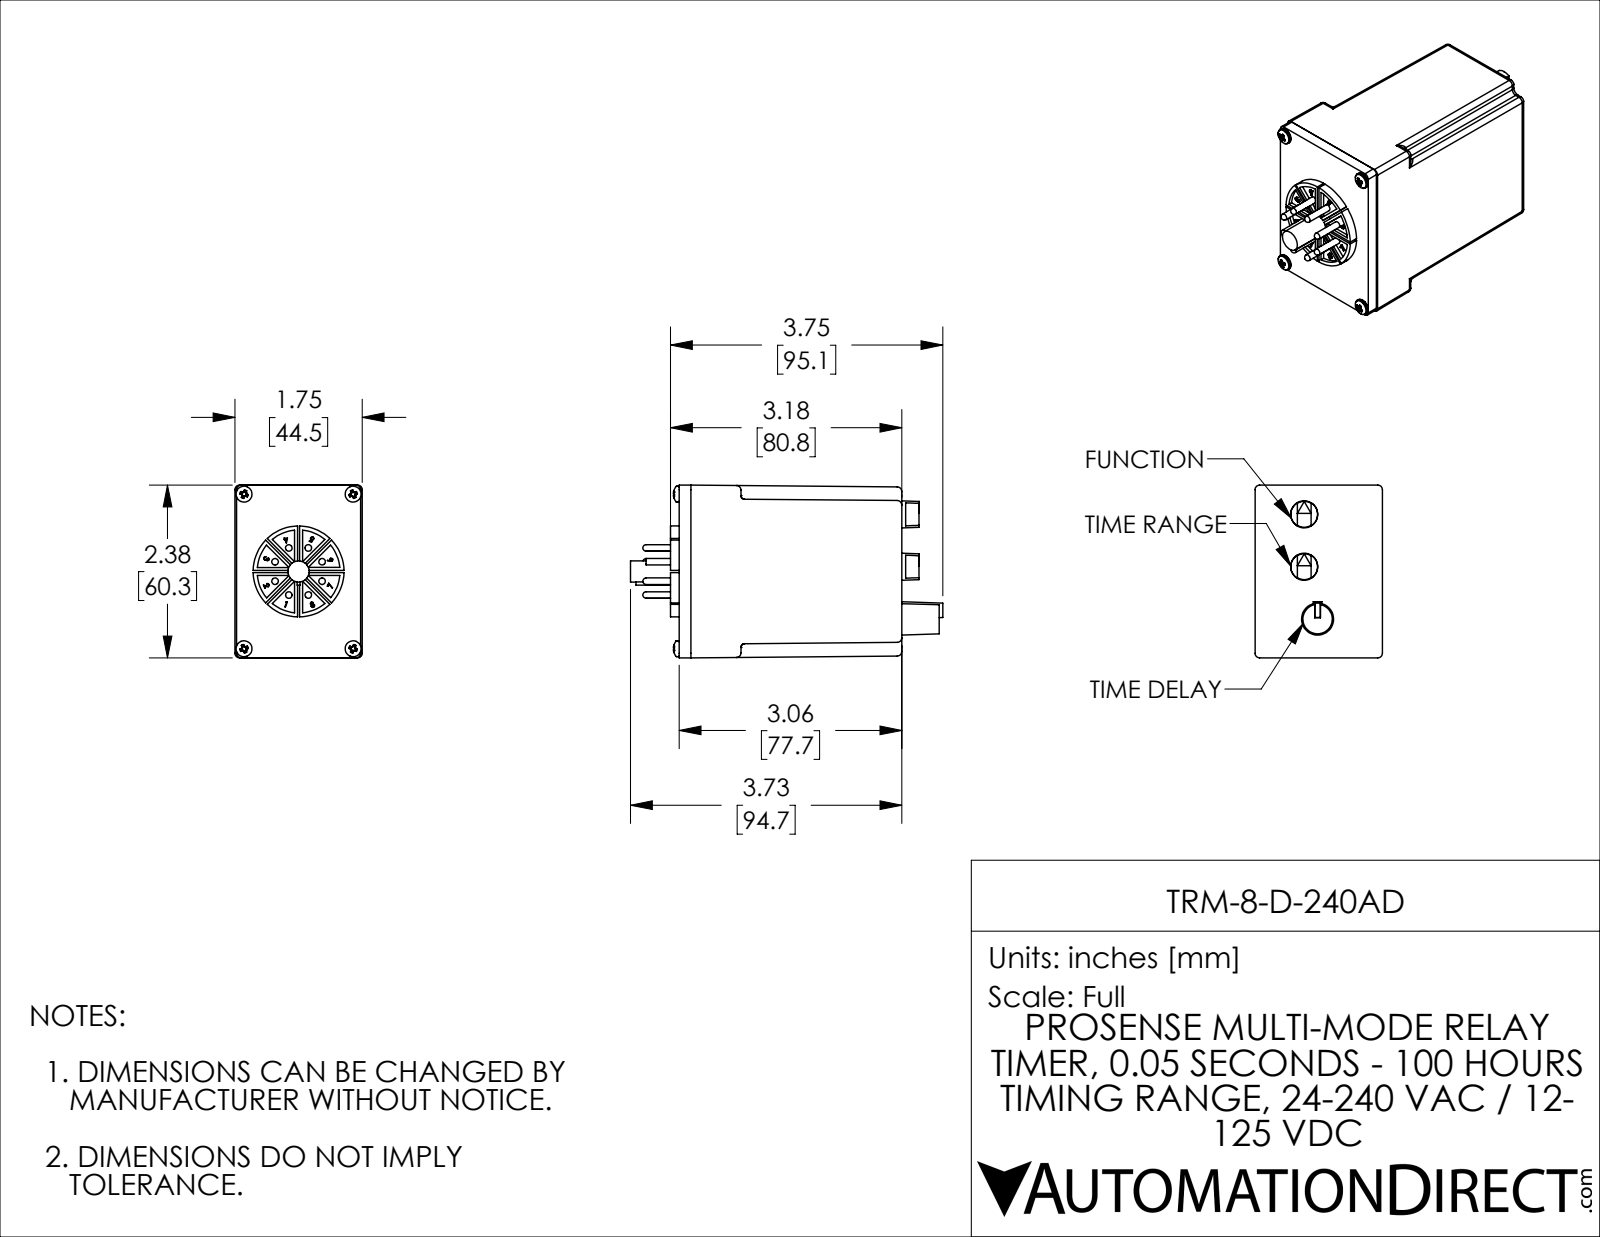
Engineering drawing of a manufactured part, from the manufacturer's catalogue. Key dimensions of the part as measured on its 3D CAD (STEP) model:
Part name (STEP PRODUCT): TRM-8-D-240AD
STEP written by: SolidWorks 2021 (CONFIG_CONTROL_DESIGN)
Units: inches
Bodies: 17 solids, 568 faces (243 planar, 164 cylindrical, 161 other)
Overall size (bounding box): 4.295 × 2.375 × 1.75
Volume: 12.34 in³ · Surface area: 46.11 in²
Round holes (diameter × count): ⌀0.125 ×4
Round bosses / shafts (diameter × count): ⌀0.09 ×8, ⌀0.219 ×4, ⌀1.25 ×1, ⌀0.29 ×1
Partial cylindrical surfaces — rounded edges, fillets, slot ends (radius × count): R0.063 ×32, R0.005 ×8, R0.05 ×4, R0.57 ×1
Main face-to-face distances: 2.9, 0.16, 3.06, 0.07, 0.23, 3.13, 0.12, 0.188, 0.05, 0.28
Hole centre spacings: 1.5, 2.125, 2.601
